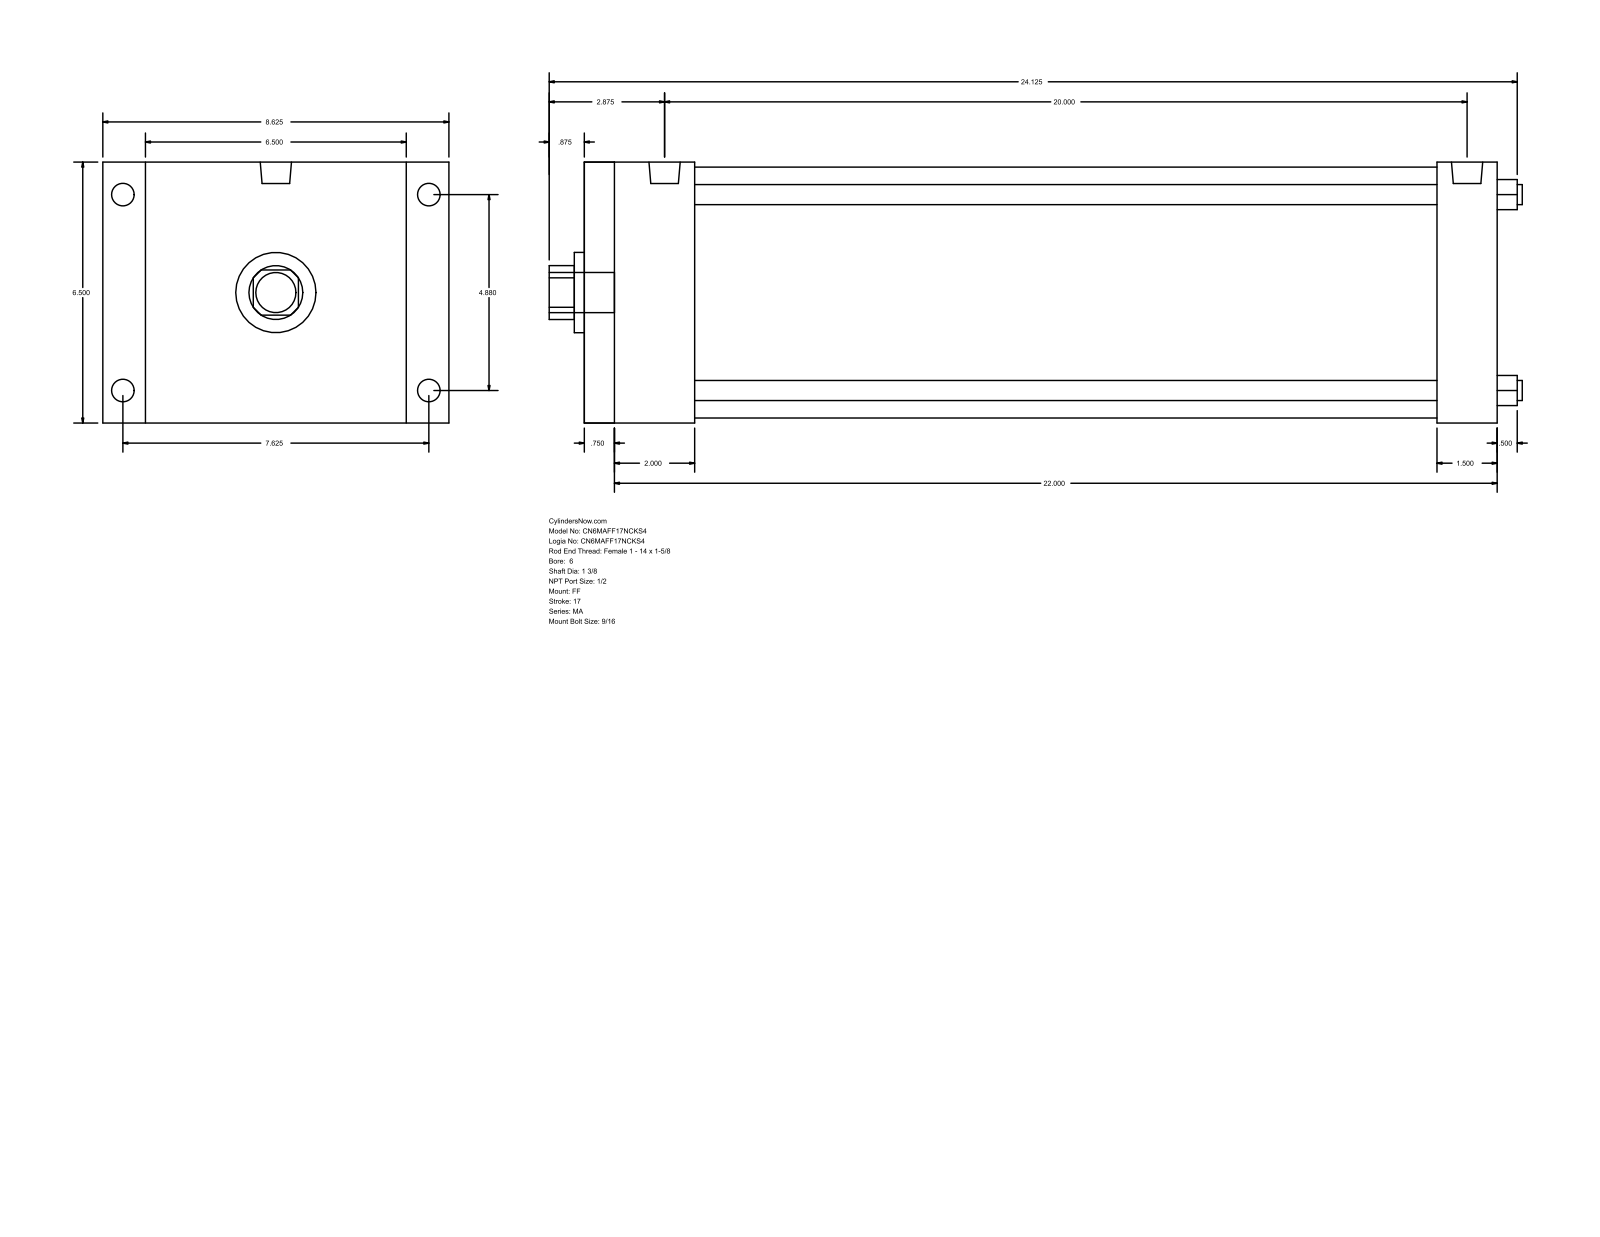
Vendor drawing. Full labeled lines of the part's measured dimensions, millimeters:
Part name (STEP PRODUCT): MA_FF__0600_1.375
STEP written by: GSSL Pune (CONFIG_CONTROL_DESIGN)
Units: millimetres
Bodies: 0 solids, 92 faces (64 planar, 28 cylindrical, 0 other)
Overall size (bounding box): 615.95 × 219.07 × 165.1
Round holes (diameter × count): ⌀12.7 ×4, ⌀34.92 ×1, ⌀50.8 ×1, ⌀158.75 ×1
Round bosses / shafts (diameter × count): ⌀17.46 ×4, ⌀14.29 ×4, ⌀19.77 ×2, ⌀25.4 ×1
Partial cylindrical surfaces — rounded edges, fillets, slot ends (radius × count): R17.06 ×1
Main face-to-face distances: 165.1, 577.85, 15.87, 561.98, 38.1, 66.67, 50.8, 511.18, 539.75, 523.88
Hole centre spacings: 87.65, 123.96, 175.31
